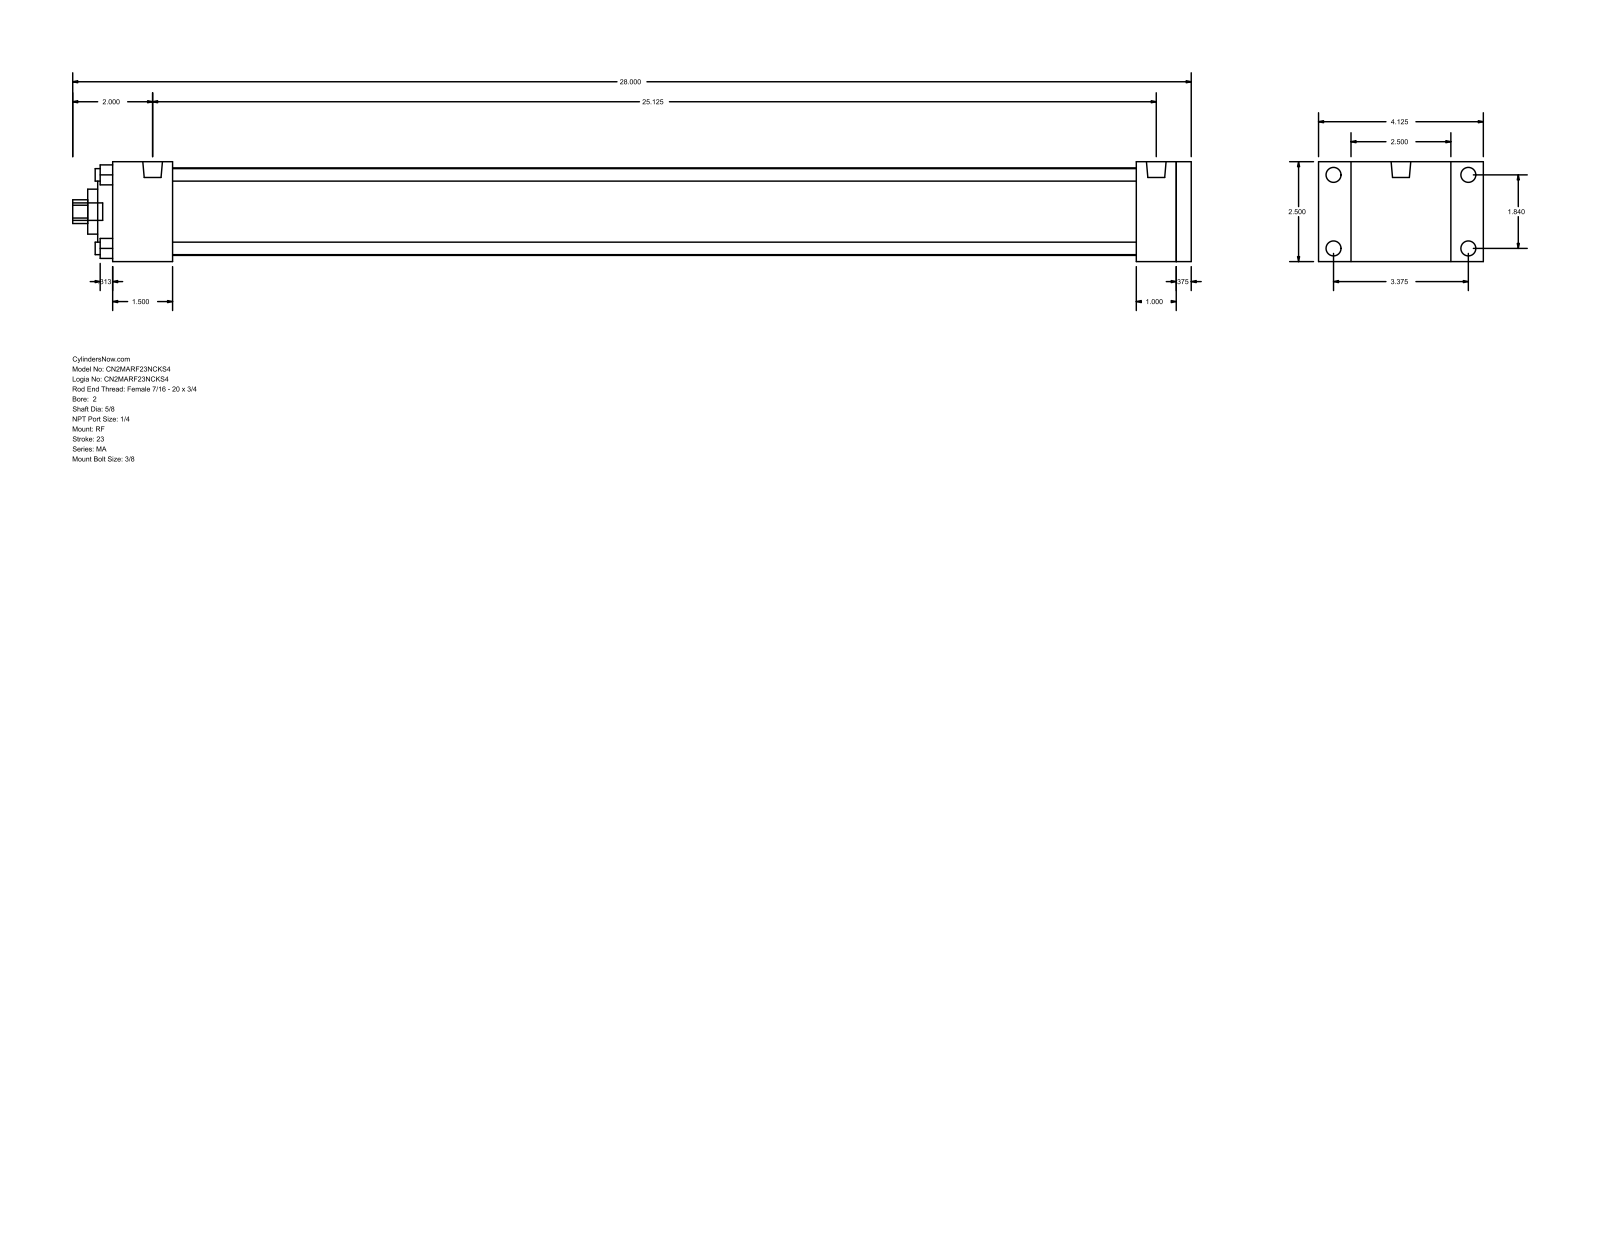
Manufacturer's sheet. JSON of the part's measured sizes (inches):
{"part_name": "MA_RF__0200_0.625", "step_written_by": "GSSL Pune (CONFIG_CONTROL_DESIGN)", "units": "inches", "bodies": {"solids": 0, "faces": 94, "planar": 65, "cylindrical": 29, "other": 0}, "overall_size": [28, 4.125, 2.5], "round_holes": [[0.313, 4], [0.625, 1], [1.125, 1], [2, 1], [2.19, 1]], "round_bosses_or_shafts": [[0.375, 4], [0.313, 4], [0.492, 2], [0.437, 1]], "partial_cylinders_radius": [[0.297, 1]], "face_to_face_distances": [2.5, 0.375, 1, 1.5, 26.625, 0.375, 27, 27.375, 25.125, 25.5], "hole_center_spacings": [1.301, 1.84, 2.602]}
